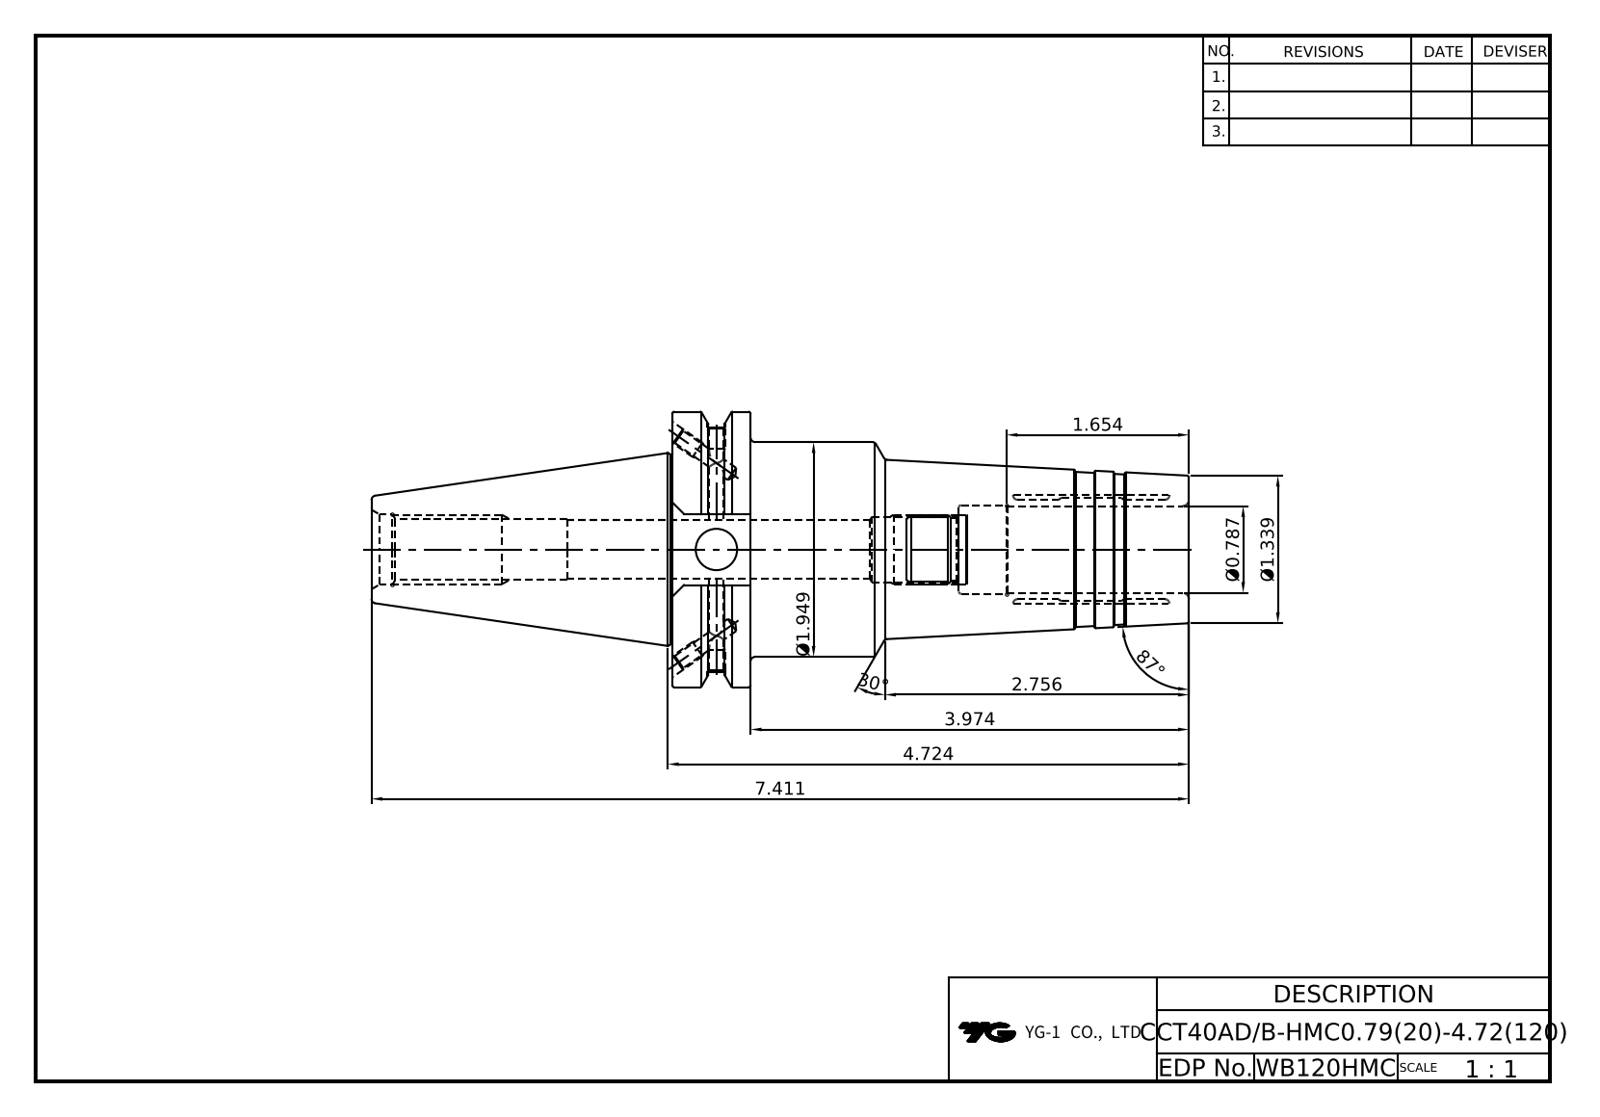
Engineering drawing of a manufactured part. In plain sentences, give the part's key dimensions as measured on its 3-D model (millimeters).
The part is named "LO-CCT40ADB-HMC20-120". Its 3-D file was written by "Autodesk Inventor 2022 (AUTOMOTIVE_DESIGN)". It is 1 solid with 106 faces: 35 planar, 30 cylindrical and 41 other. Overall it measures 188.25 by 63.5 by 61.09 millimeters. Its volume is 216 367 cubic millimeters and its surface area 38 779 square millimeters. Round holes: 4 of diameter 3.24, 2 of diameter 4, 2 of diameter 4.2, 1 of diameter 9.53, 1 of diameter 13, 1 of diameter 13.39, 1 of diameter 14.92, 1 of diameter 16.3, 1 of diameter 20, 1 of diameter 20.6. Round bosses or shafts: 1 of diameter 63.5, 1 of diameter 49.5, 1 of diameter 43.8. Partial cylindrical surfaces (rounded edges, fillets, slot ends): 1 of radius 8.19, 1 of radius 28.15. The main face-to-face distances are 18.05, 119, 100.95, 47.6, 16.38, 66, 47.95, 53, 69.25, 87.3.
